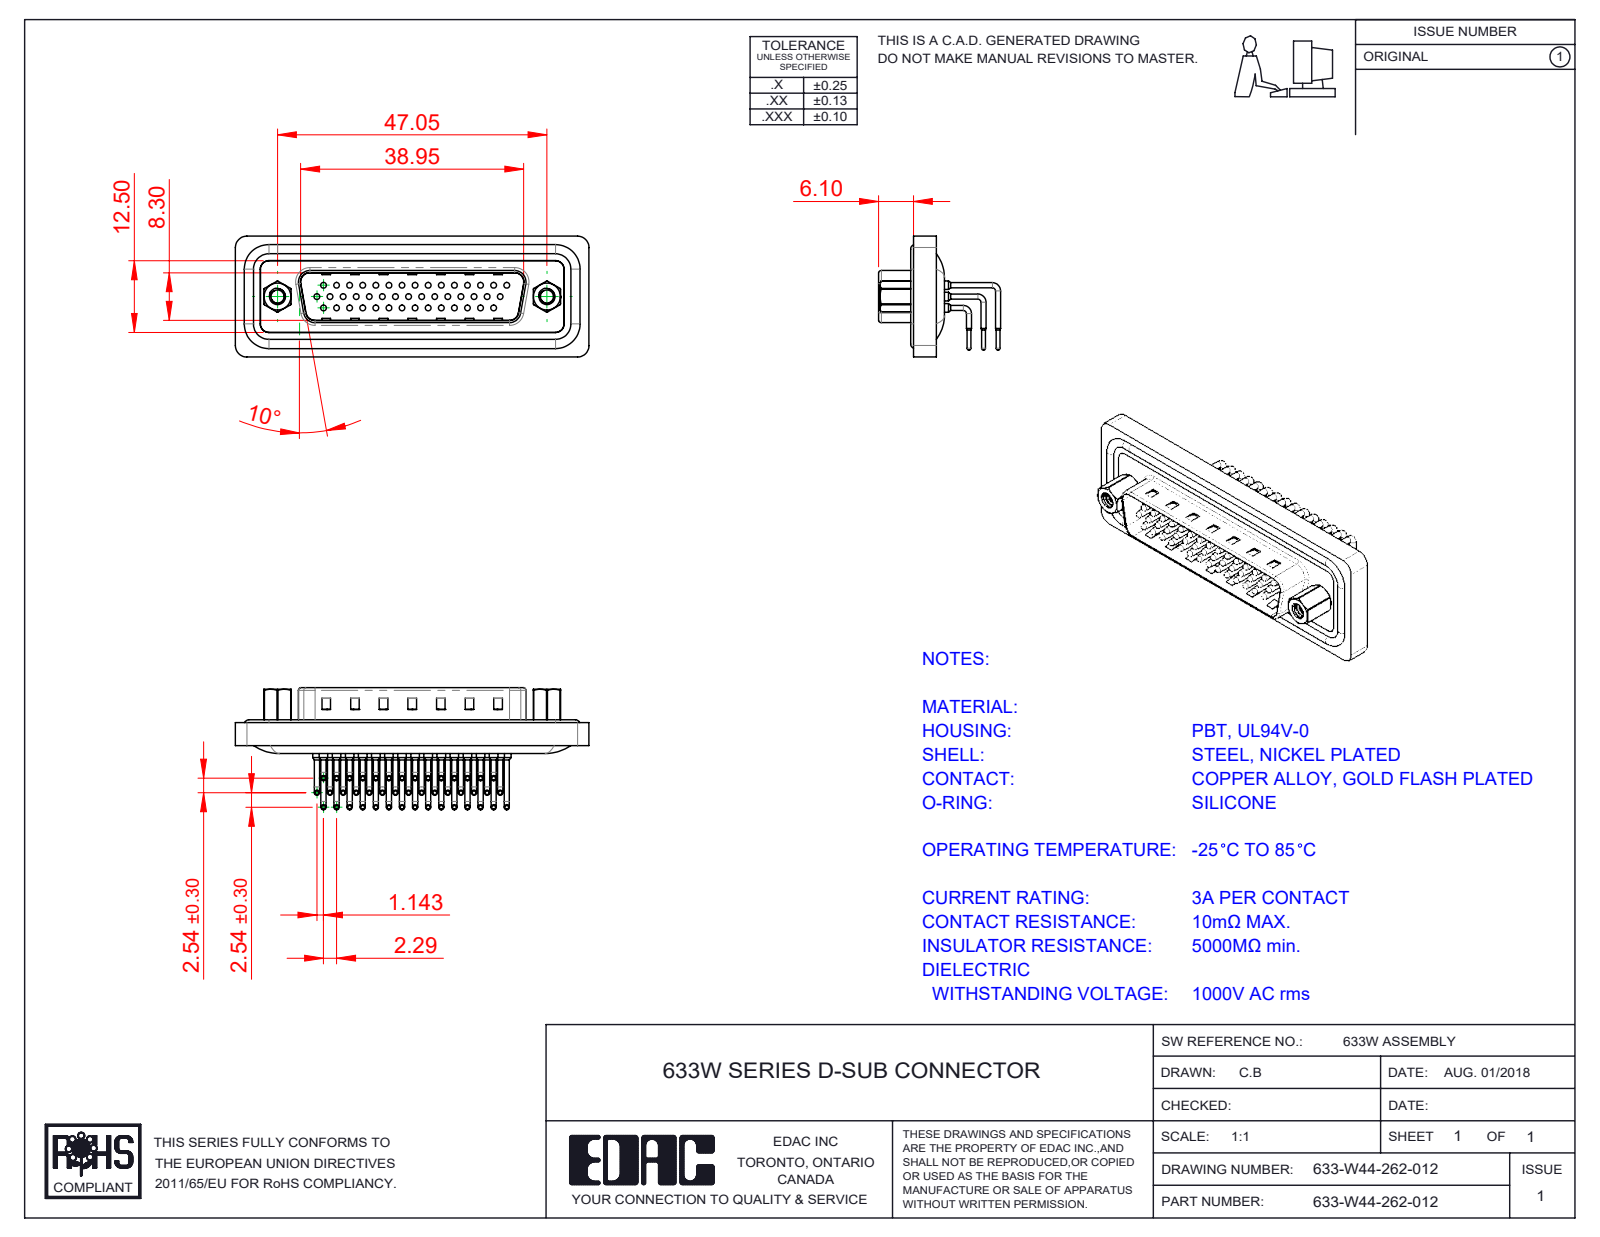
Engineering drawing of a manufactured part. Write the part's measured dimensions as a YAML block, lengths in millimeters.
part_name: "633W 4-40 Hex Standoff; 633W Contact Row 1; 633-W44-262-012; 633W Housing_44 Contacts (+5 more)"
step_written_by: "SolidWorks 2023 (CONFIG_CONTROL_DESIGN)"
units: millimeters
bodies: {solids: 52, faces: 5440, planar: 3021, cylindrical: 1886, other: 533}
overall_size: [61.74, 21.52, 21.1]
volume: 6674
surface_area: 13581
round_holes:
  - {diameter: 1, count: 44}
  - {diameter: 1.5, count: 44}
  - {diameter: 1.7, count: 44}
  - {diameter: 2, count: 44}
  - {diameter: 2.26, count: 2}
  - {diameter: 2.29, count: 2}
  - {diameter: 4, count: 2}
  - {diameter: 4.8, count: 2}
  - {diameter: 5, count: 2}
round_bosses_or_shafts:
  - {diameter: 0.9, count: 88}
  - {diameter: 0.65, count: 44}
  - {diameter: 1.5, count: 18}
  - {diameter: 1.6, count: 4}
  - {diameter: 4.9, count: 2}
  - {diameter: 2.79, count: 2}
  - {diameter: 5, count: 1}
partial_cylinders:
  - {radius: 1.01, count: 44}
  - {radius: 2, count: 14}
  - {radius: 1.5, count: 13}
  - {radius: 0.5, count: 8}
  - {radius: 2.7, count: 6}
  - {radius: 0.9, count: 4}
  - {radius: 1.6, count: 4}
  - {radius: 4.3, count: 4}
face_to_face_distances: [0.4, 1.6, 2.5, 2.9, 1.1, 5.65, 15.45, 14.7, 6.4, 0.75]
hole_center_spacings: [2.28, 3.96, 2.29, 4.57, 8.24, 6.86, 11.43, 14.99]
